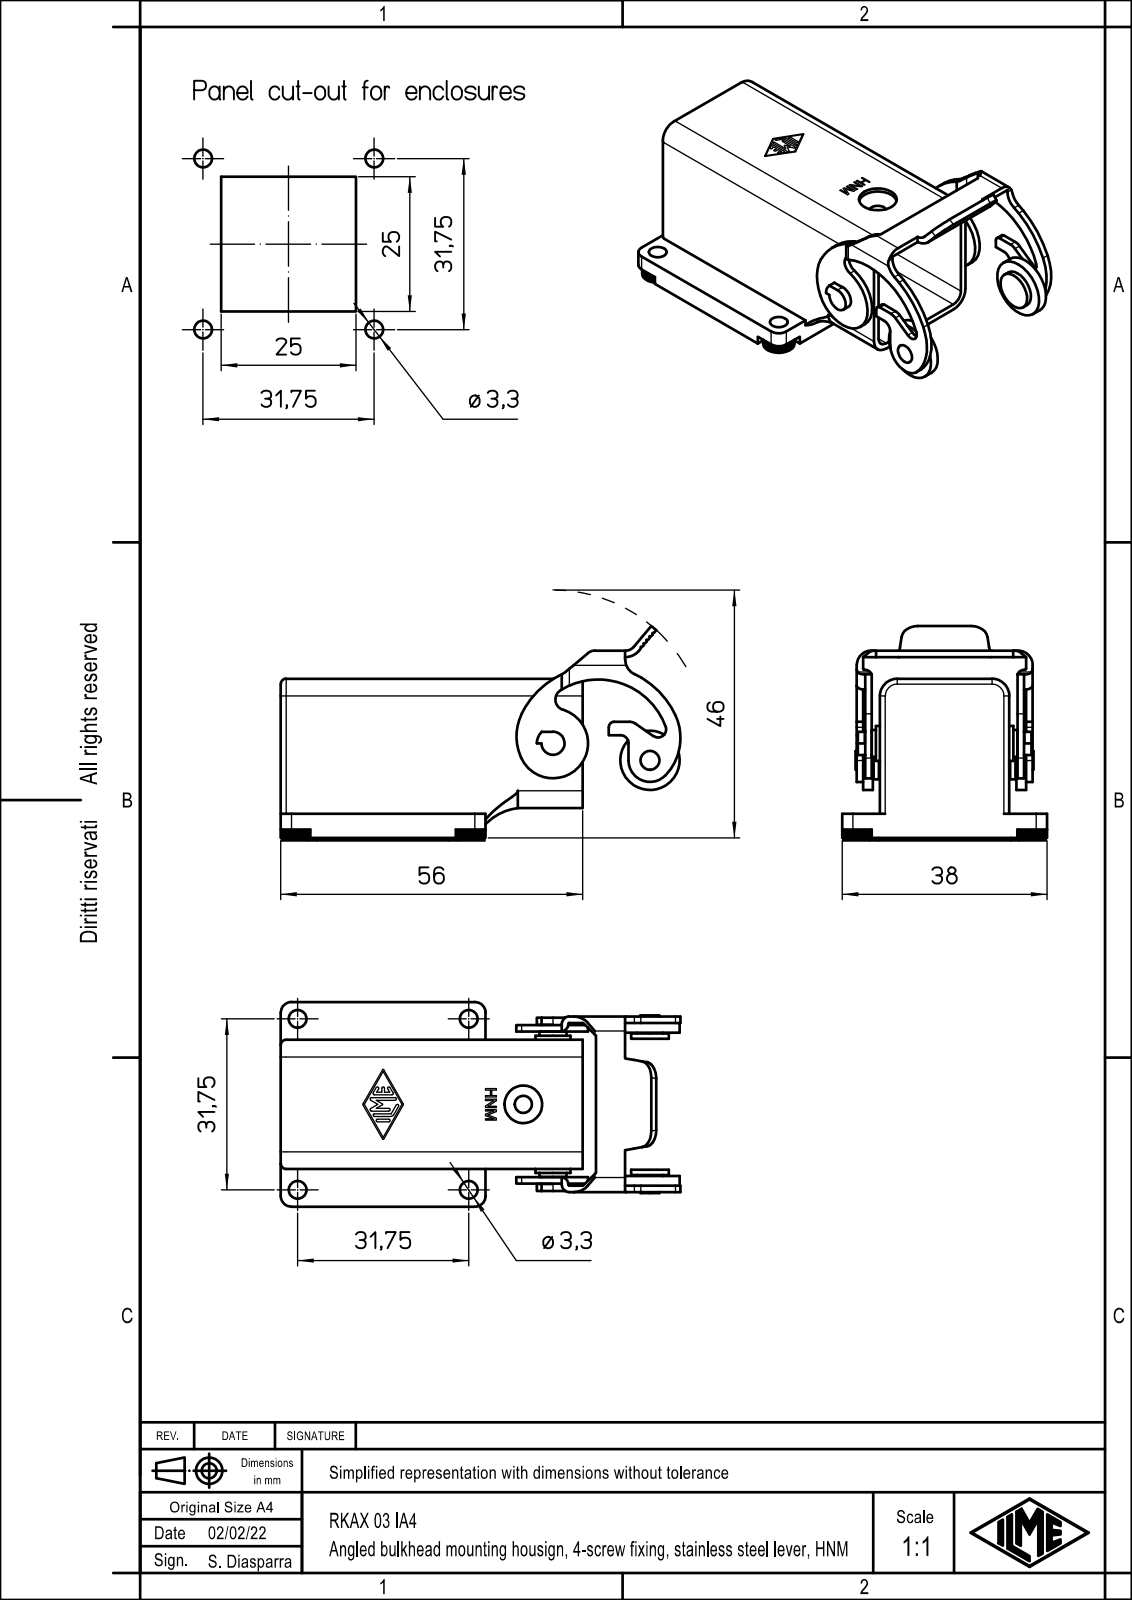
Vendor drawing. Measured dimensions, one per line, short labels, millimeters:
name: RKAX_03_IA4
written by: Creo Elements/Direct Modeling 20.1B 02-Apr-2019 (C) Parametric Technology GmbH (AUTOMOTIVE_DESIGN)
unit: mm
bodies: 1 solid, 328 faces (178 planar, 143 cylindrical, 7 other)
size: 74.16 × 39.8 × 38
volume: 14 321 mm³; area: 15 046 mm²
holes: 4× ⌀3.1, 4× ⌀3.3, 1× ⌀3.2, 1× ⌀7
bosses: 1× ⌀11, 1× ⌀7, 1× ⌀6.5, 1× ⌀5, 1× ⌀4.8, 1× ⌀4.3, 1× ⌀3.5
rounds: 16× R2, 15× R0.25, 9× R3.2, 5× R3, 4× R1, 4× R1.4, 4× R2.9, 3× R0.12
face distances: 1.2, 22.8, 21.6, 24, 25.05, 23.85, 2.25, 5, 30, 4.95
hole spacings: 31.76, 18.83, 44.79, 44.92, 31.75, 44.78, 44.91
